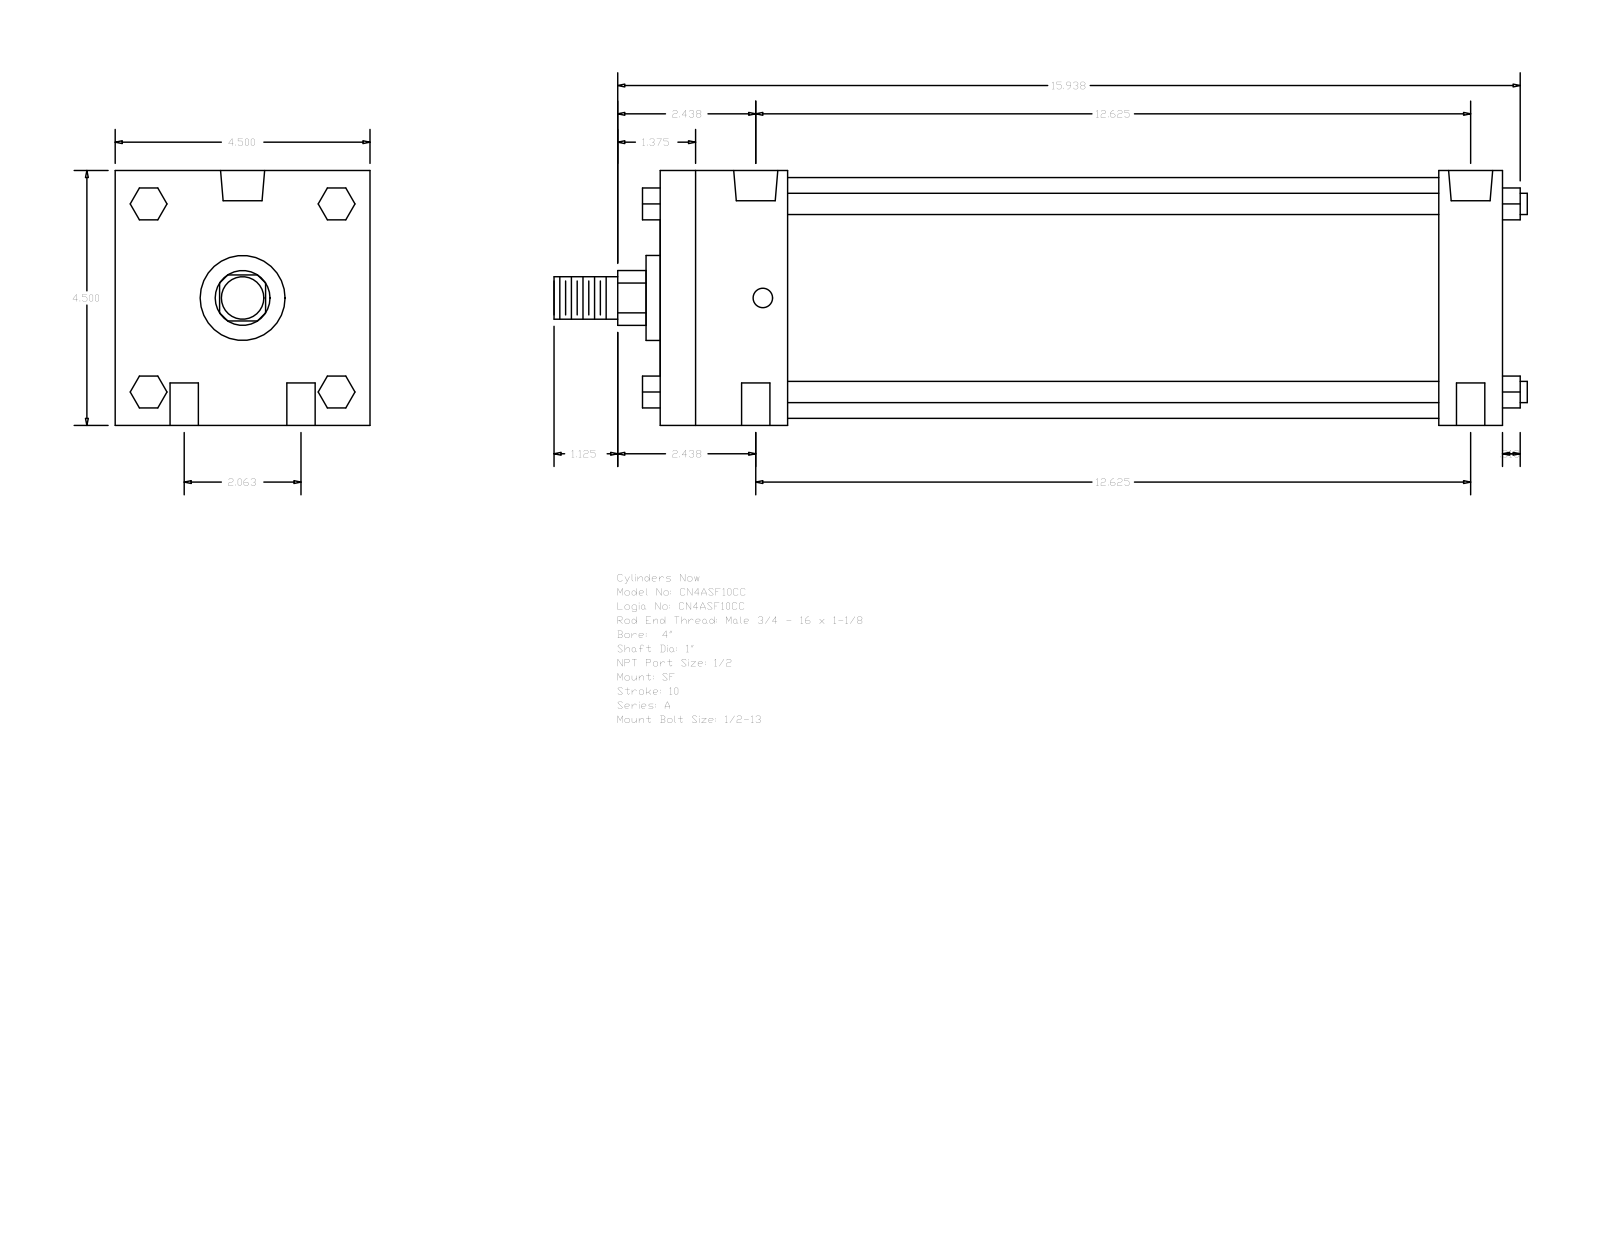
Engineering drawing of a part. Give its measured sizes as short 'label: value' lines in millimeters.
name: A_SF__0400_1
written by: GSSL Pune (CONFIG_CONTROL_DESIGN)
unit: mm
bodies: 0 solids, 124 faces (94 planar, 30 cylindrical, 0 other)
size: 436.56 × 114.3 × 114.3
holes: 4× ⌀12.7, 2× ⌀8.73, 2× ⌀19.77
bosses: 4× ⌀9.53, 1× ⌀107.95, 1× ⌀38.1, 1× ⌀25.4, 1× ⌀19.05
rounds: 1× R12.29
face distances: 114.3, 377.83, 349.25, 28.58, 57.15, 292.1, 320.68, 14.29, 42.16, 73.03
hole spacings: 26.19, 321.75, 320.68, 52.38, 324.93, 314.32
